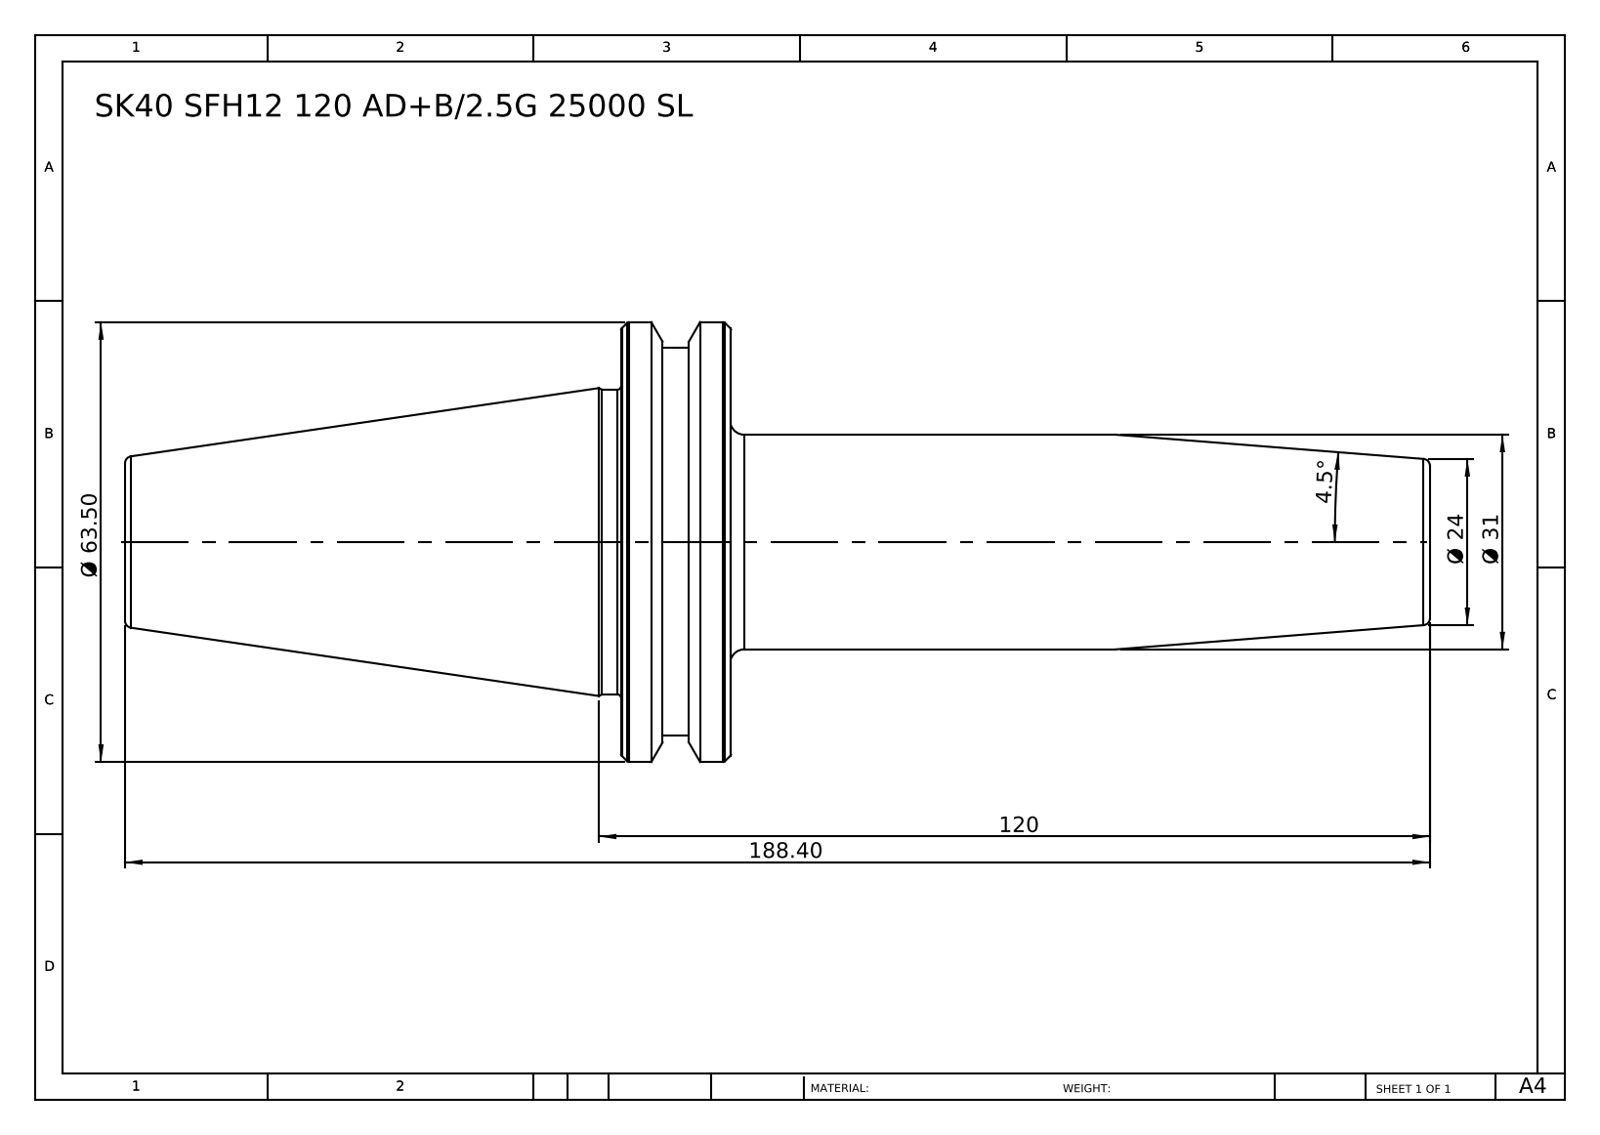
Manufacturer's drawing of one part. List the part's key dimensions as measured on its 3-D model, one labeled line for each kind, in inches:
Part name (STEP PRODUCT): SK40 SFH12 120 AD+B-2.5G 25000 SL
STEP written by: SolidWorks 2014 (CONFIG_CONTROL_DESIGN)
Units: inches
Bodies: 1 solid, 46 faces (6 planar, 10 cylindrical, 30 other)
Overall size (bounding box): 7.417 × 2.5 × 2.5
Volume: 11.35 in³ · Surface area: 40.07 in²
Round bosses / shafts (diameter × count): ⌀2.5 ×1, ⌀2.205 ×1, ⌀1.732 ×1, ⌀1.22 ×1
Main face-to-face distances: 0.626, 3.445, 2.819, 3.972, 4.598, 7.417, 4.213, 0.24, 0.386, 3.205
